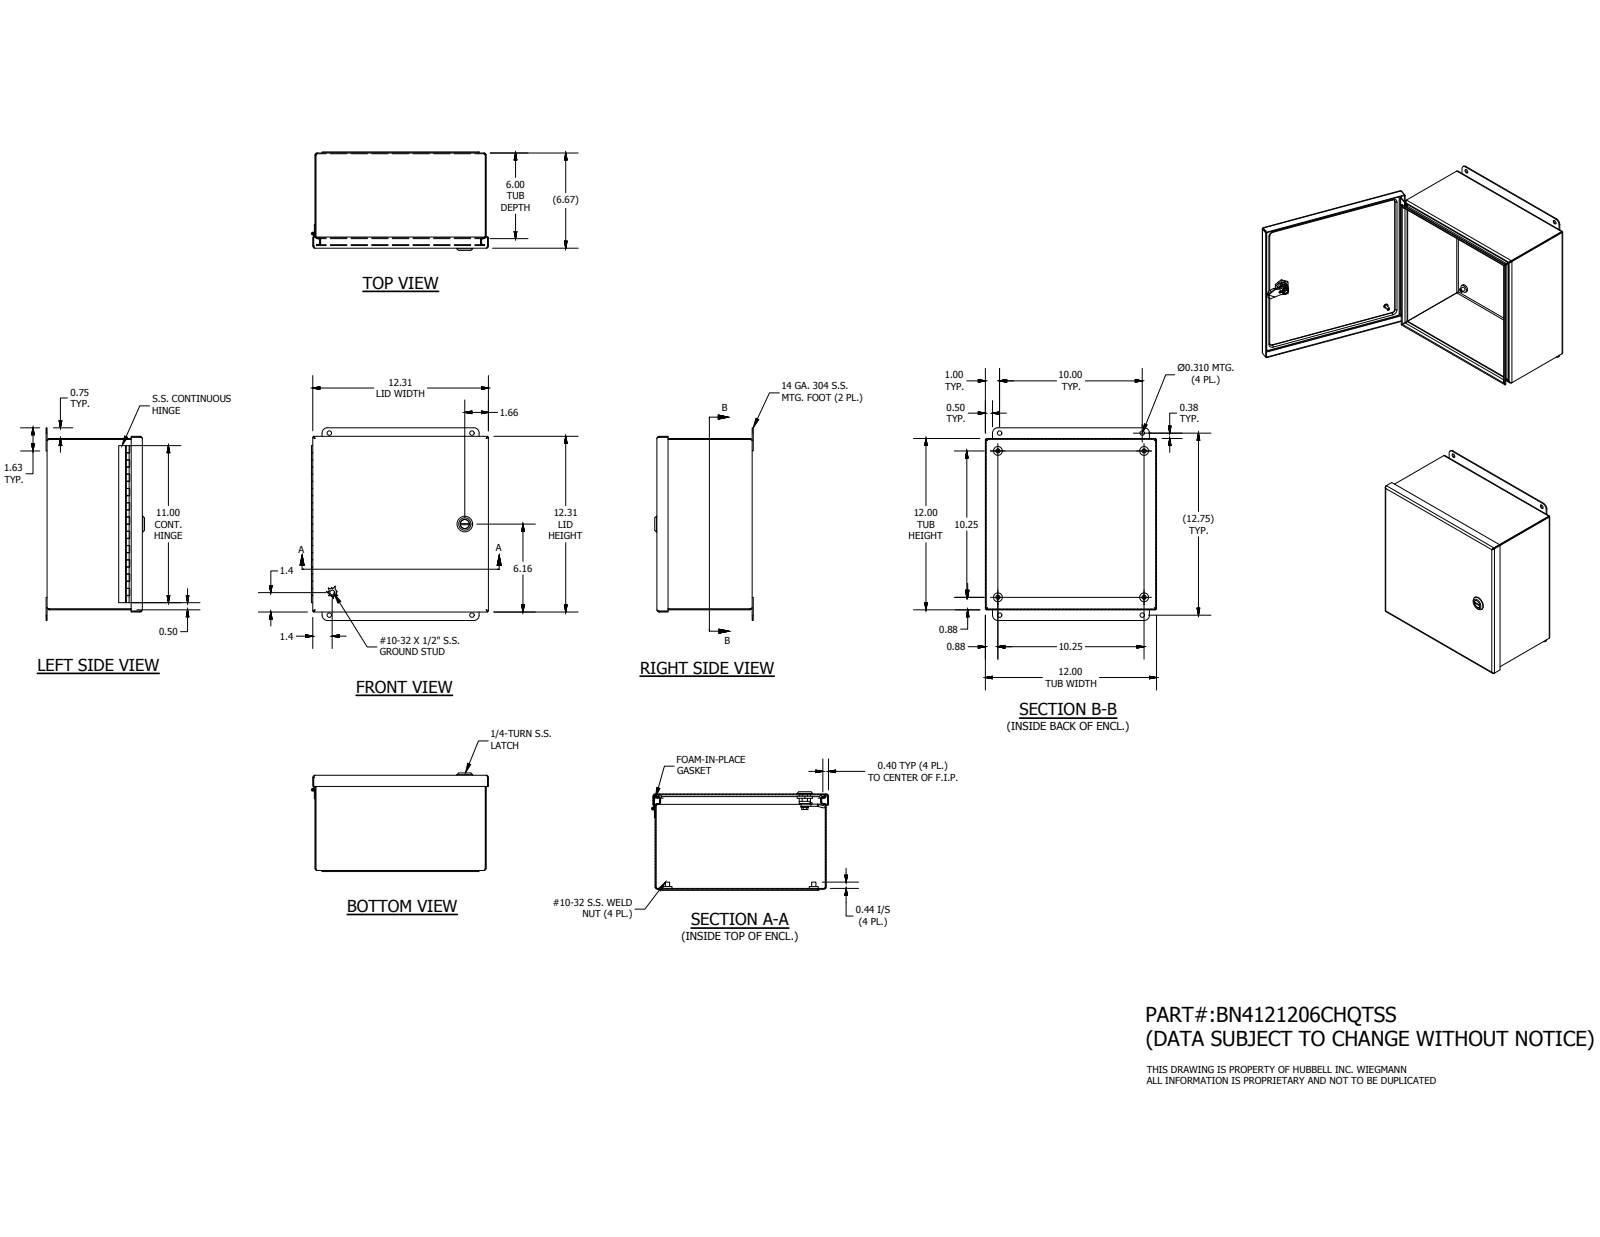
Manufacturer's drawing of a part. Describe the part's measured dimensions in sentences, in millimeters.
The part is named "BN41212CHQTSSLID; 12x12; 34856; H4050551LH (+8 more)". Its 3-D file was written by "Autodesk Inventor 2016 (AUTOMOTIVE_DESIGN)". It is 19 solids with 628 faces: 335 planar, 199 cylindrical and 94 other. Overall it measures 342.9 by 315.26 by 175.39 millimeters. Its volume is 767 071 cubic millimeters and its surface area 962 840 square millimeters. Round holes: 4 of diameter 3.96, 4 of diameter 7.87, 1 of diameter 2.96, 1 of diameter 5, 1 of diameter 8, 1 of diameter 10, 1 of diameter 10.2, 1 of diameter 16.1. Round bosses or shafts: 4 of diameter 15.88, 4 of diameter 7.62, 1 of diameter 28, 1 of diameter 19.8, 1 of diameter 16, 1 of diameter 15.2, 1 of diameter 13.5, 1 of diameter 12.8. Partial cylindrical surfaces (rounded edges, fillets, slot ends): 20 of radius 2.38, 20 of radius 3.88, 16 of radius 3.17, 8 of radius 0.5, 4 of radius 4, 4 of radius 9.53, 2 of radius 2.31, 1 of radius 6.45. The main face-to-face distances are 1.5, 1.49, 303.3, 167.99, 169.48, 166.49, 167.98, 304.8, 303.31, 301.81. The hole center spacings are 31.91, 260.35, 292.12, 389.18, 131.14, 254, 259.12, 259.13.
